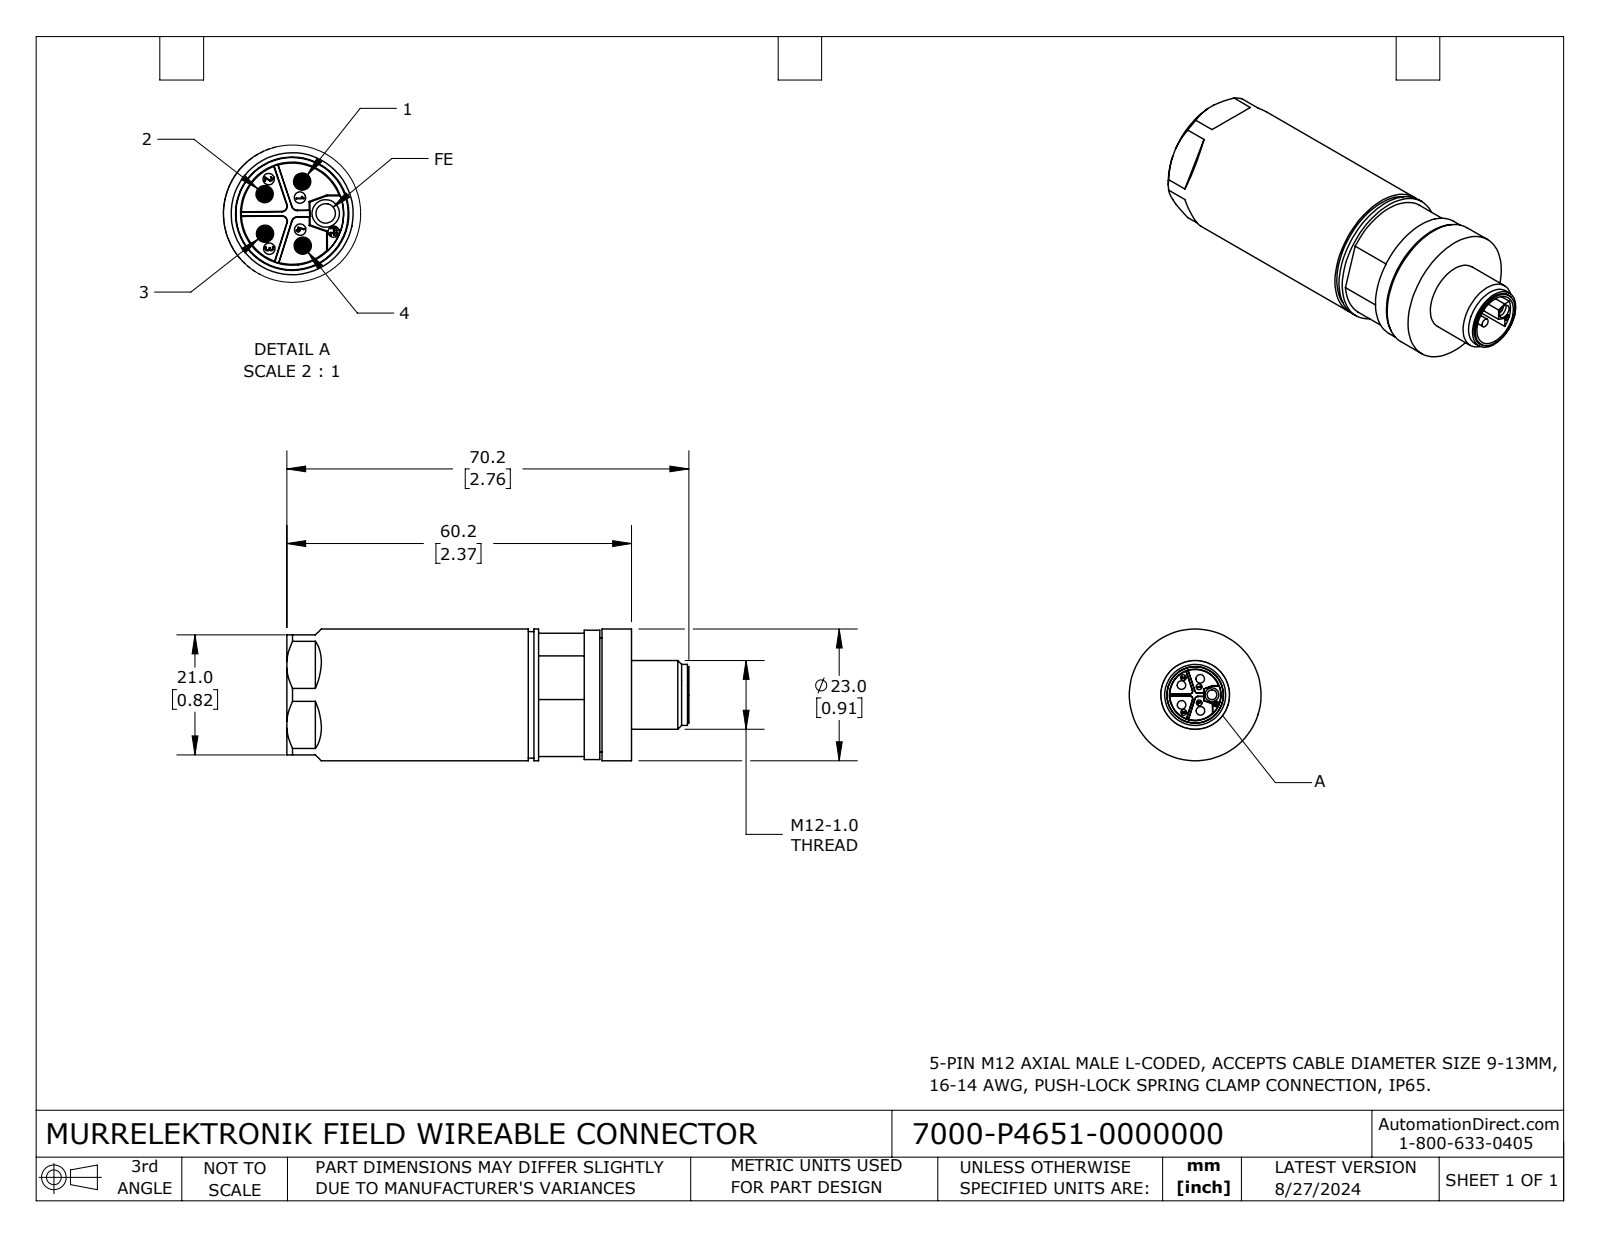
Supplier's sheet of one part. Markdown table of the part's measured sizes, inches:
| quantity | value |
| --- | --- |
| part name | 7000-P4651-0000000 |
| STEP written by | SolidWorks 2023 (CONFIG_CONTROL_DESIGN) |
| units | inches |
| bodies | 2 solids, 245 faces (113 planar, 111 cylindrical, 21 other) |
| overall size | 2.764 × 0.906 × 0.906 |
| volume | 1.389 in³ |
| surface area | 15.37 in² |
| round holes (diameter × count) | 0.039 × 4, 0.039 × 1, 0.067 × 1, 0.094 × 1, 0.327 × 1, 0.39 × 1, 0.701 × 1 |
| round bosses / shafts (diameter × count) | 0.059 × 4, 0.906 × 1, 0.89 × 1, 0.87 × 1, 0.787 × 1, 0.597 × 1, 0.472 × 1, 0.419 × 1 |
| partial cylindrical surfaces (radius × count) | 0.004 × 4, 0.007 × 3, 0.007 × 2, 0.006 × 1, 0.008 × 1, 0.372 × 1, 0.423 × 1 |
| main face-to-face distances | 2.37, 0.055, 0.039, 0.203, 2.167, 2.315, 2.112, 0.134, 0.421, 0.453 |
| hole center spacings | 0.061, 0.144, 0.229, 0.069, 0.104, 0.104, 0.11, 0.115 |
